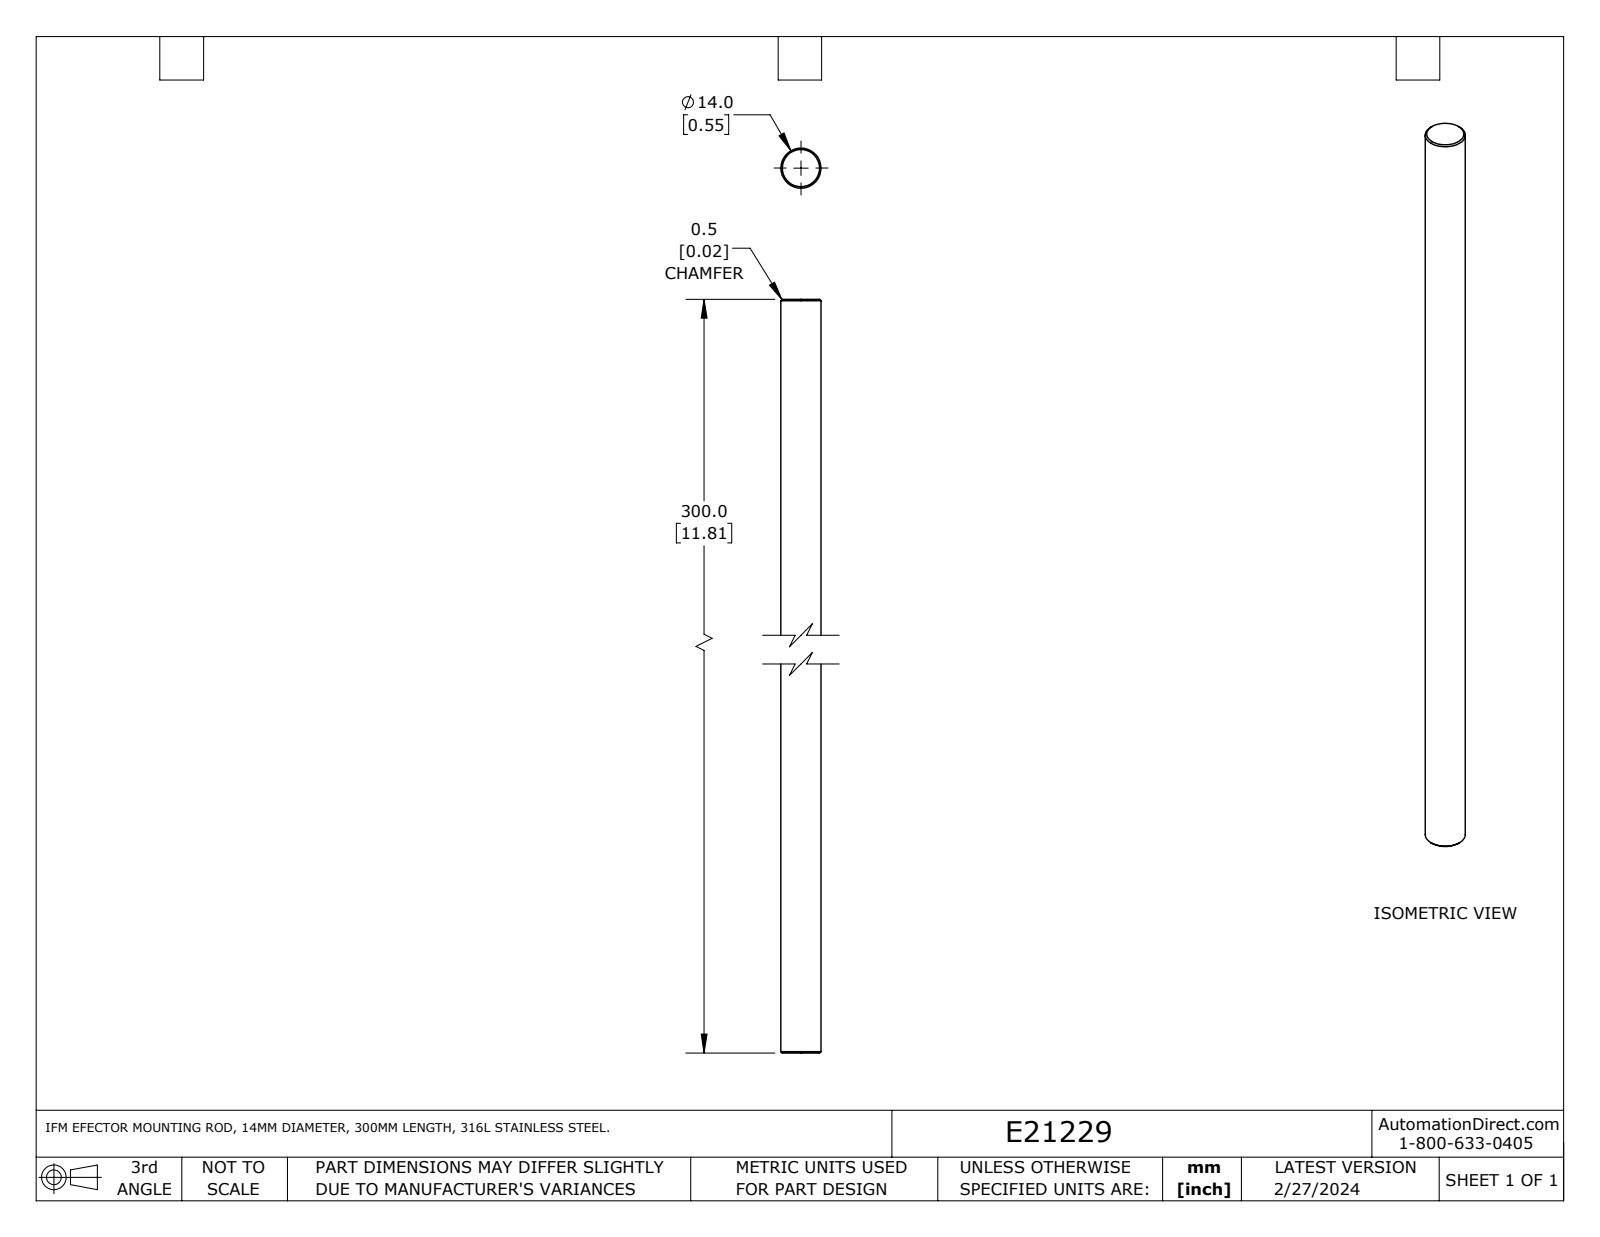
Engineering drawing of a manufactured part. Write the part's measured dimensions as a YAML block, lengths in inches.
part_name: "E21229"
step_written_by: "SolidWorks 2023 (AUTOMOTIVE_DESIGN)"
units: inches
bodies: {solids: 1, faces: 5, planar: 2, cylindrical: 1, other: 2}
overall_size: [11.811, 0.551, 0.551]
volume: 2.818
surface_area: 20.89
round_bosses_or_shafts:
  - {diameter: 0.551, count: 1}
face_to_face_distances: [11.811]
